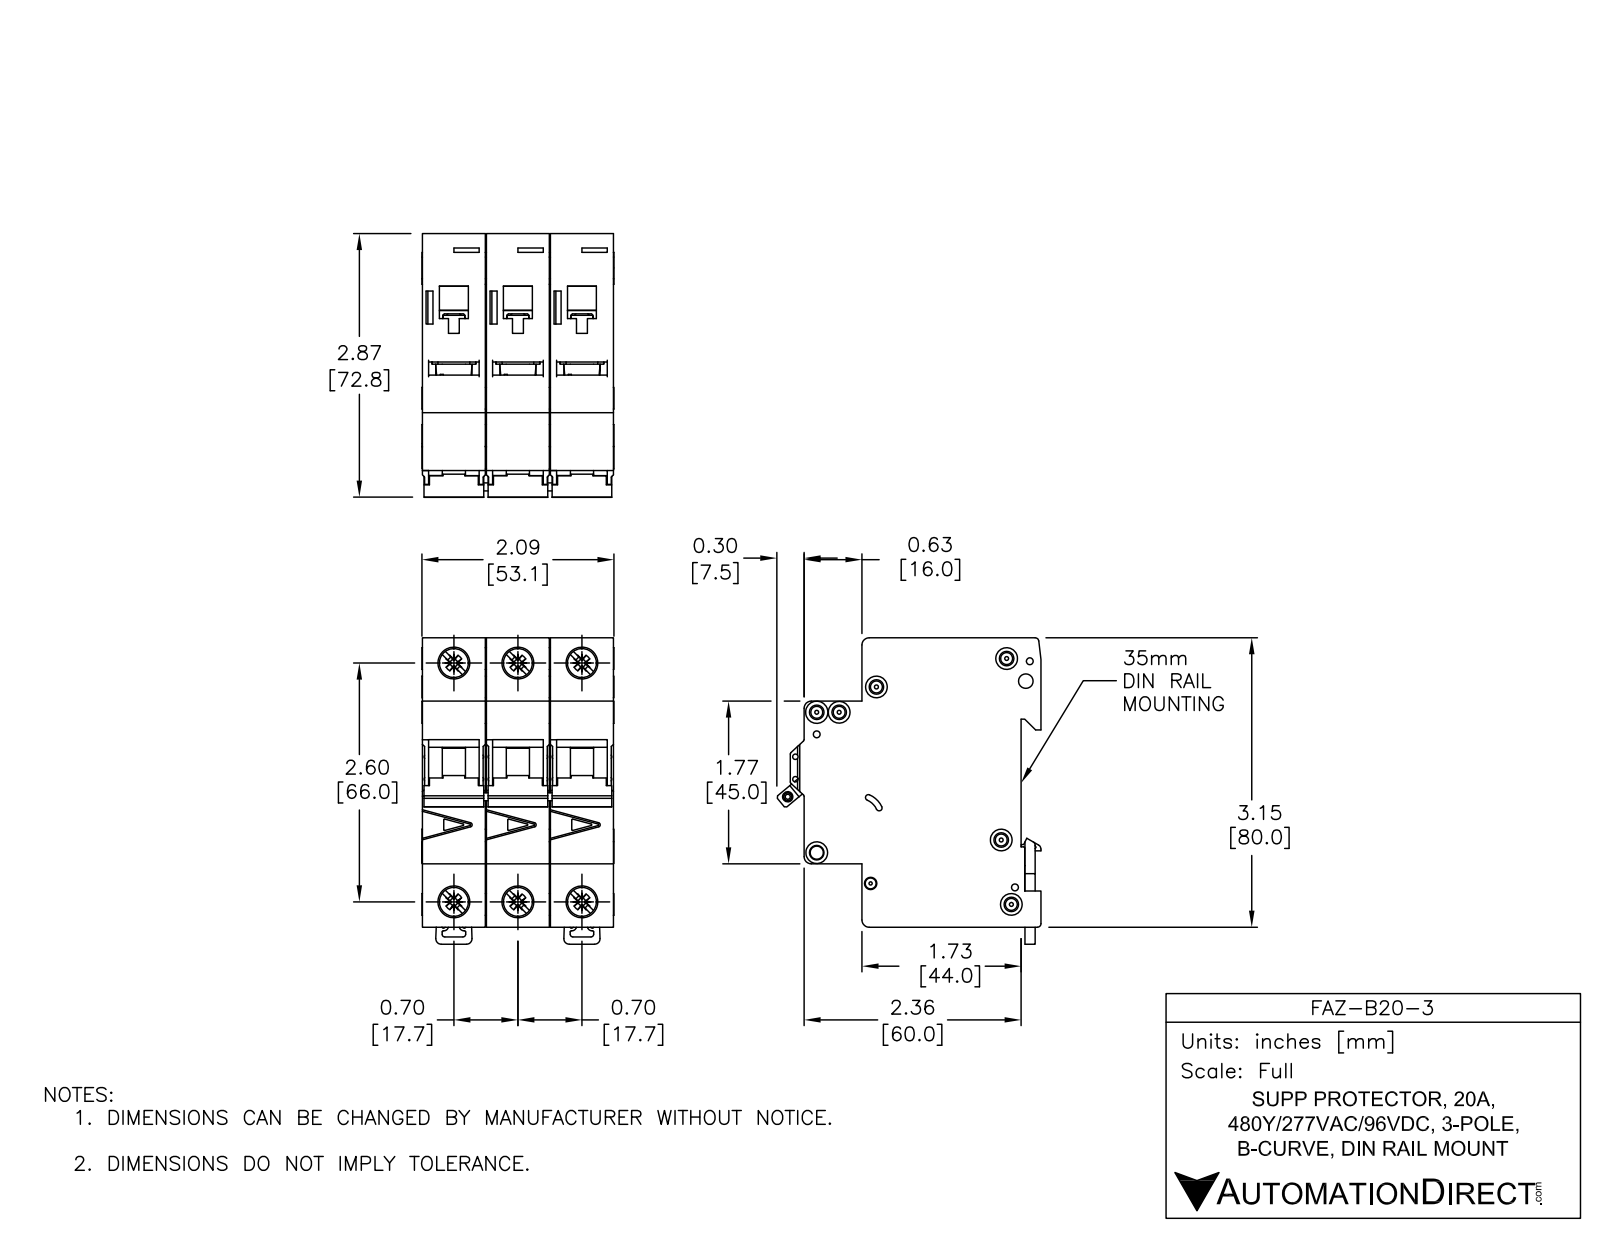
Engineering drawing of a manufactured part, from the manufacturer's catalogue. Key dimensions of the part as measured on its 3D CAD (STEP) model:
Part name (STEP PRODUCT): FAZ-B20-3
STEP written by: SolidWorks 2014 (AUTOMOTIVE_DESIGN)
Units: millimetres
Bodies: 11 solids, 1650 faces (697 planar, 590 cylindrical, 363 other)
Overall size (bounding box): 84.78 × 73.04 × 53.1
Volume: 224 680 mm³ · Surface area: 58 052 mm²
Round holes (diameter × count): ⌀3.6 ×6, ⌀8.2 ×4, ⌀1.9 ×3, ⌀1.09 ×2, ⌀1.5 ×2, ⌀4 ×2, ⌀7.15 ×2, ⌀2.15 ×1, ⌀2.2 ×1, ⌀2.55 ×1, ⌀3.3 ×1, ⌀3.4 ×1
Round bosses / shafts (diameter × count): ⌀6 ×4, ⌀2.5 ×3, ⌀8.2 ×2
Partial cylindrical surfaces — rounded edges, fillets, slot ends (radius × count): R0.25 ×68, R0.5 ×25, R1 ×12, R2 ×12, R0.2 ×11, R1.8 ×3, R0.8 ×2, R3 ×2
Main face-to-face distances: 17.7, 17.5, 35.4, 35.2, 52.9, 17.9, 79.48, 5.5, 49.5, 44
Hole centre spacings: 17.7, 68.33, 66, 6.2, 13.64, 35.4, 74.89, 4.81
